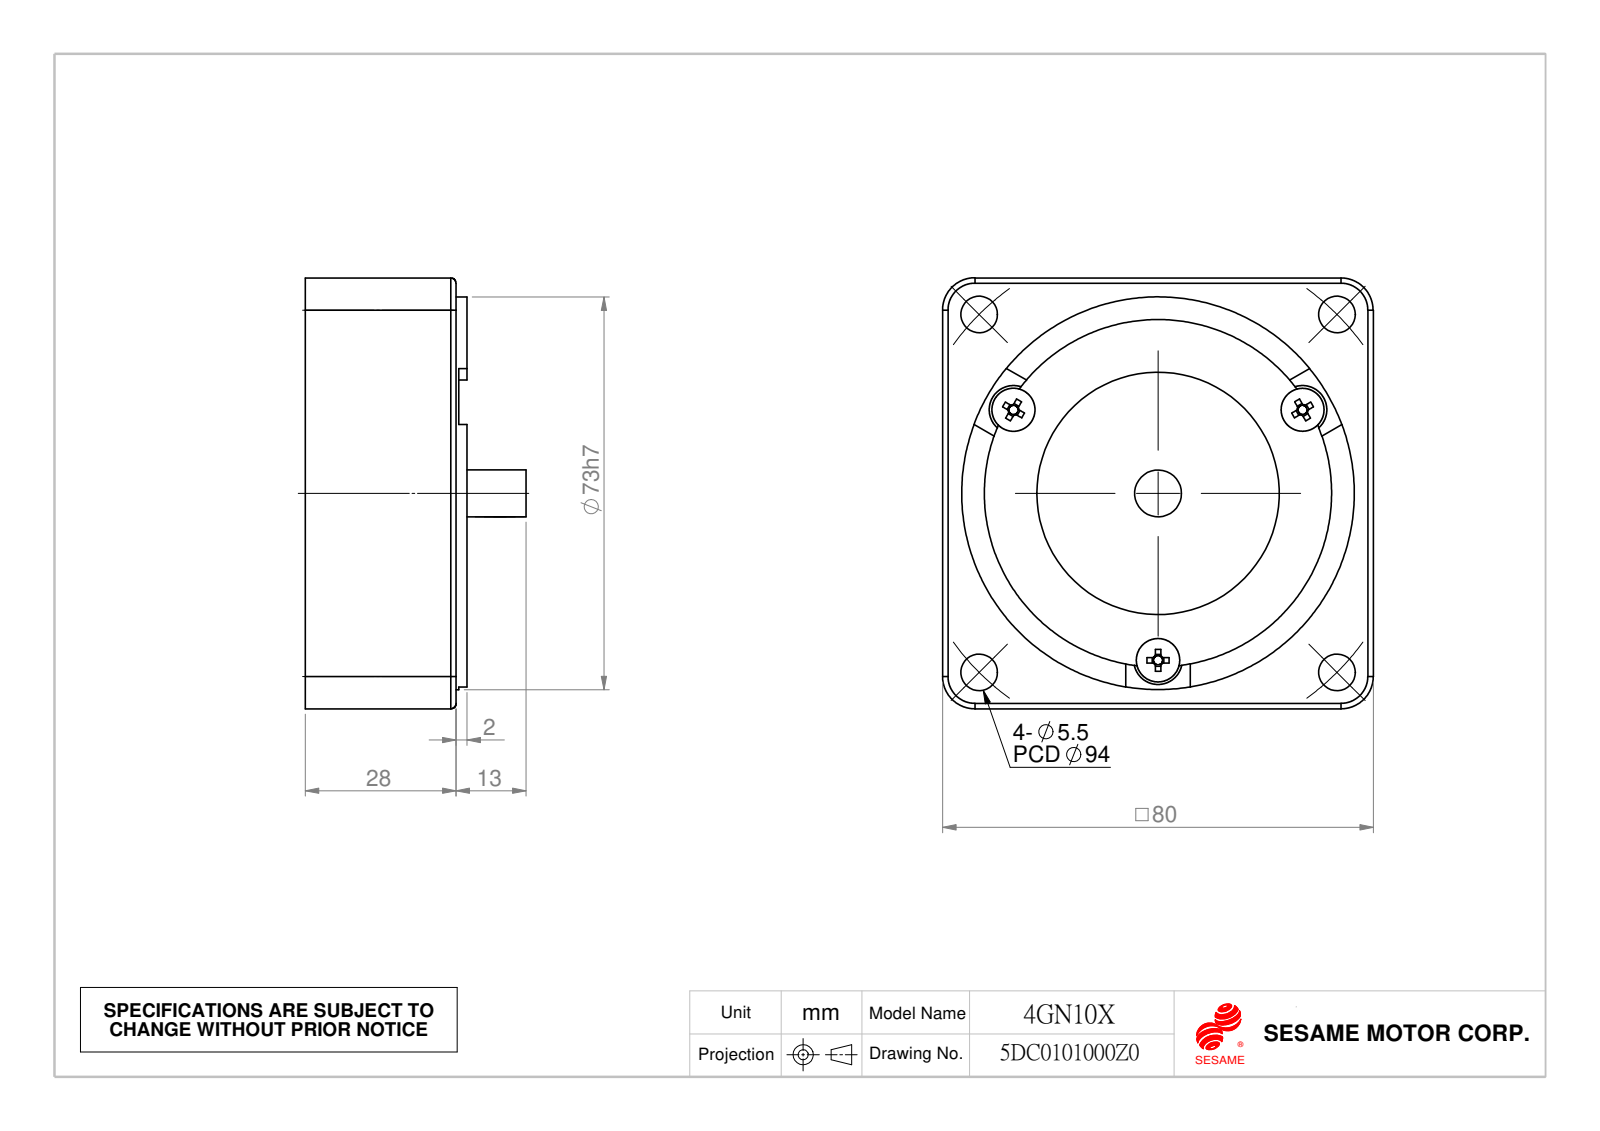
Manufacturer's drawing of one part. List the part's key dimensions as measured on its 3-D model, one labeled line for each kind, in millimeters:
Part name (STEP PRODUCT): STP4x12_JIS B 1111 Binding head screw M4 x 8 --8N; G473-M_加工圖; FT158
STEP written by: SolidWorks 2010 (CONFIG_CONTROL_DESIGN)
Units: millimetres
Bodies: 11 solids, 630 faces (134 planar, 222 cylindrical, 274 other)
Overall size (bounding box): 80 × 80 × 41
Volume: 148 766 mm³ · Surface area: 40 980 mm²
Round holes (diameter × count): ⌀5.5 ×4, ⌀15 ×4, ⌀8 ×3, ⌀3.75 ×2, ⌀3.5 ×1, ⌀6 ×1, ⌀10 ×1, ⌀13 ×1, ⌀17 ×1, ⌀64.5 ×1
Round bosses / shafts (diameter × count): ⌀7 ×4, ⌀5.4 ×4, ⌀8.3 ×3, ⌀4 ×3, ⌀72.94 ×1, ⌀72.9 ×1, ⌀45 ×1, ⌀16.95 ×1
Partial cylindrical surfaces — rounded edges, fillets, slot ends (radius × count): R5 ×10, R1 ×4, R6 ×4, R7 ×4, R36.2 ×1, R36.48 ×1
Main face-to-face distances: 2, 80, 21.5, 23, 1.5, 3.5, 21, 5, 0.5, 19.5
Hole centre spacings: 53.69, 31, 32, 44.55, 53.7, 6.66, 20, 25.2
